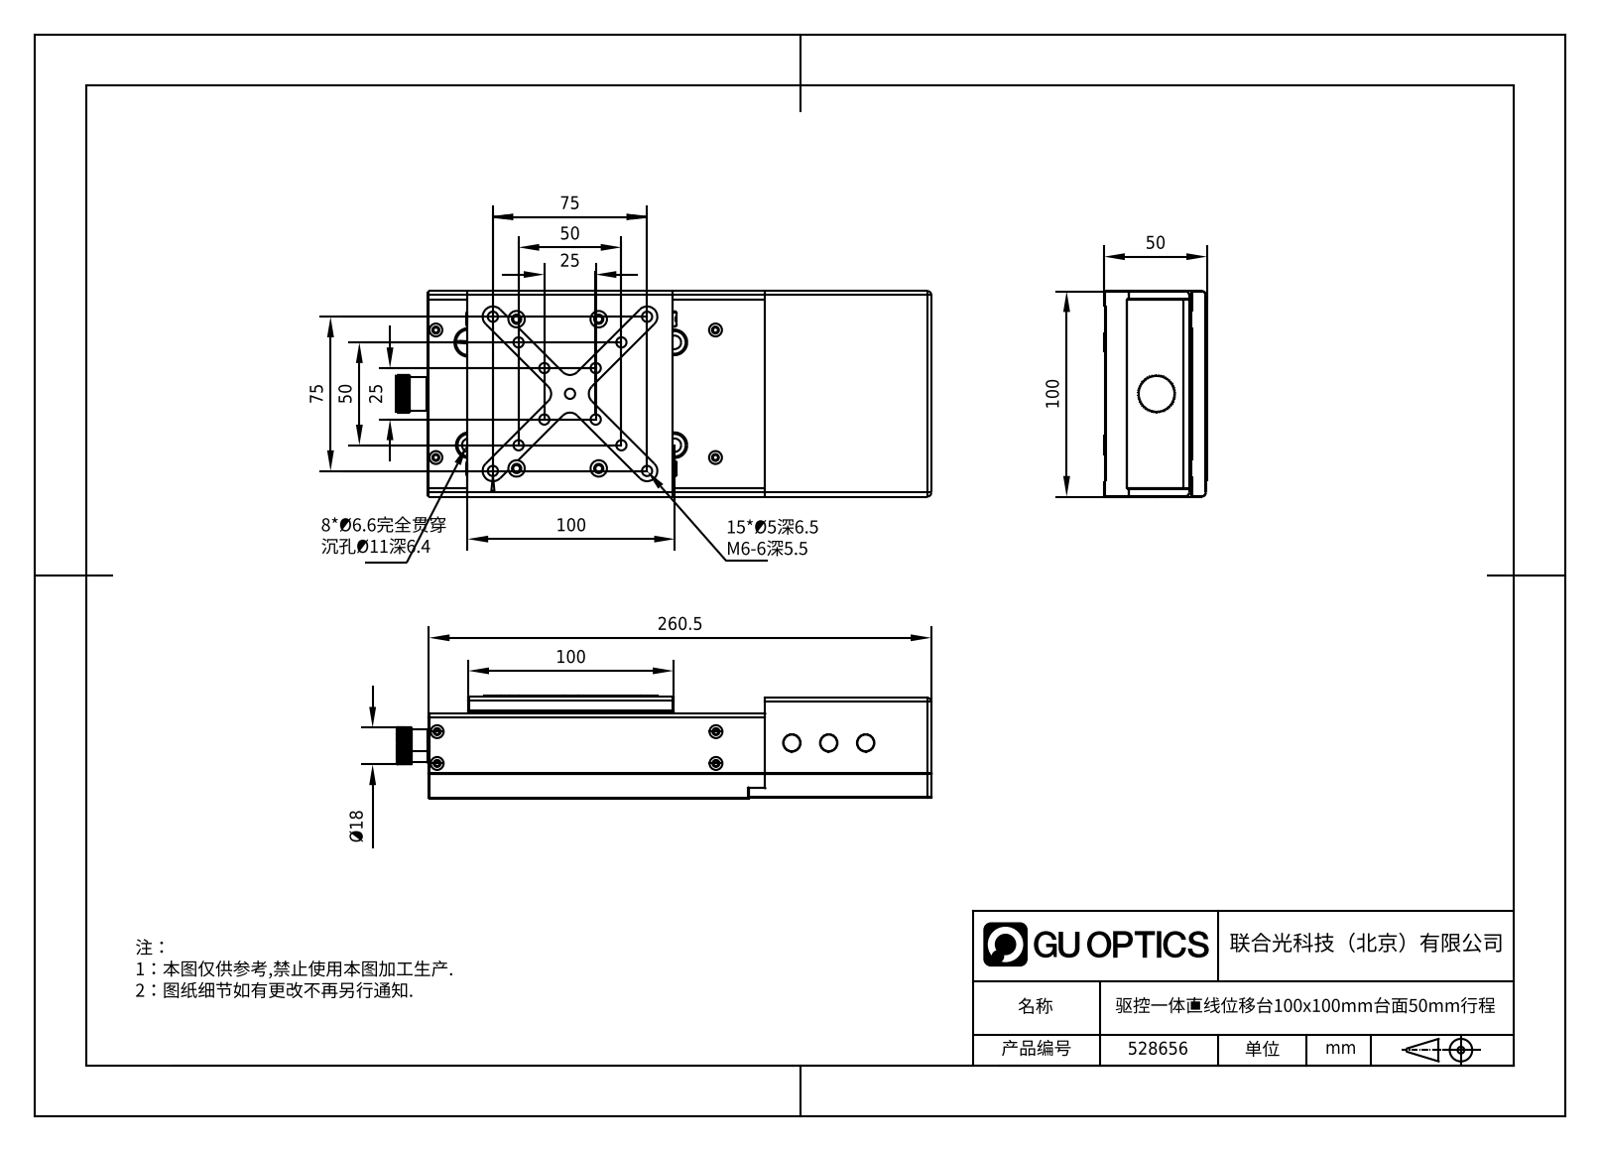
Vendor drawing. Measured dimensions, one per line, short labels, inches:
name: 528656
written by: SolidWorks 2020 (CONFIG_CONTROL_DESIGN)
unit: in
bodies: 47 solids, 2393 faces (1224 planar, 808 cylindrical, 361 other)
size: 10.256 × 3.937 × 1.969
volume: 47.7 in³; area: 416.8 in²
holes: 32× ⌀0.094, 21× ⌀0.098, 21× ⌀0.134, 18× ⌀0.165, 17× ⌀0.062, 16× ⌀0.063, 16× ⌀0.173, 14× ⌀0.197, 9× ⌀0.256, 8× ⌀0.26, 8× ⌀0.433, 8× ⌀0.492
bosses: 4× ⌀0.087, 2× ⌀0.551, 2× ⌀0.15, 2× ⌀0.079, 1× ⌀0.866, 1× ⌀0.63, 1× ⌀0.512, 1× ⌀0.118
rounds: 29× R0.079, 24× R0.039, 12× R0.197, 4× R0.028, 4× R0.053, 2× R0.012, 2× R0.016, 2× R0.02
face distances: 0.157, 1.496, 0.039, 0.276, 0.315, 1.043, 1.201, 0.453, 0.02, 1.476
hole spacings: 0.413, 0.591, 0.315, 0.472, 0.568, 1.181, 1.772, 2.858
